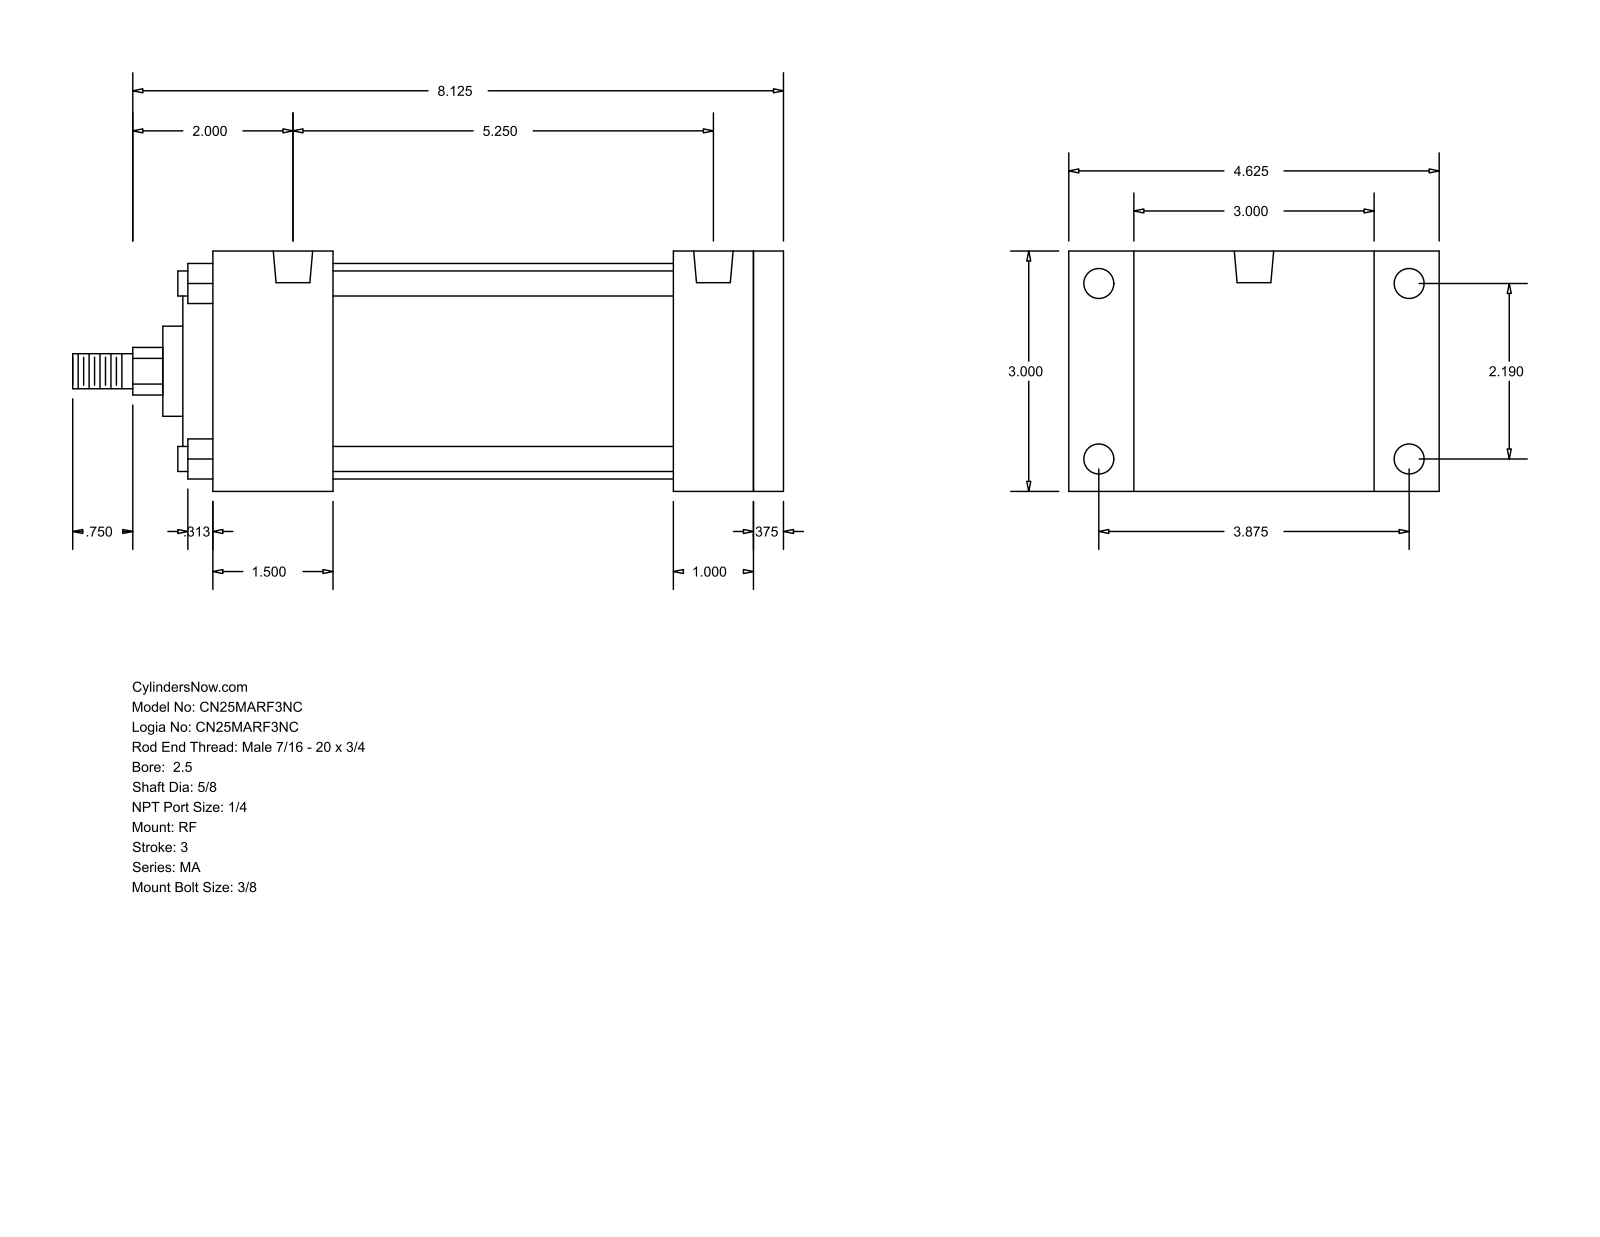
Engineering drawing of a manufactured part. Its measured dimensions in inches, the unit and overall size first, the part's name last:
Units: inches
Overall size (bounding box): 8.875 × 4.625 × 3
Round holes (diameter × count): ⌀0.313 ×4, ⌀0.375 ×4, ⌀0.492 ×2
Round bosses / shafts (diameter × count): ⌀0.313 ×4, ⌀2.69 ×1, ⌀2 ×1, ⌀1.125 ×1, ⌀0.625 ×1, ⌀0.437 ×1
Partial cylindrical surfaces — rounded edges, fillets, slot ends (radius × count): R0.297 ×1
Main face-to-face distances: 3, 7.125, 0.375, 6.75, 1, 1.375, 1.5, 5.75, 4.25, 5.25
Hole centre spacings: 2.19, 3.875, 4.451, 5.25
Bodies: 0 solids, 94 faces (65 planar, 29 cylindrical, 0 other)
Part name (STEP PRODUCT): MA_RF__0250_0.625
STEP written by: GSSL Pune (CONFIG_CONTROL_DESIGN)
